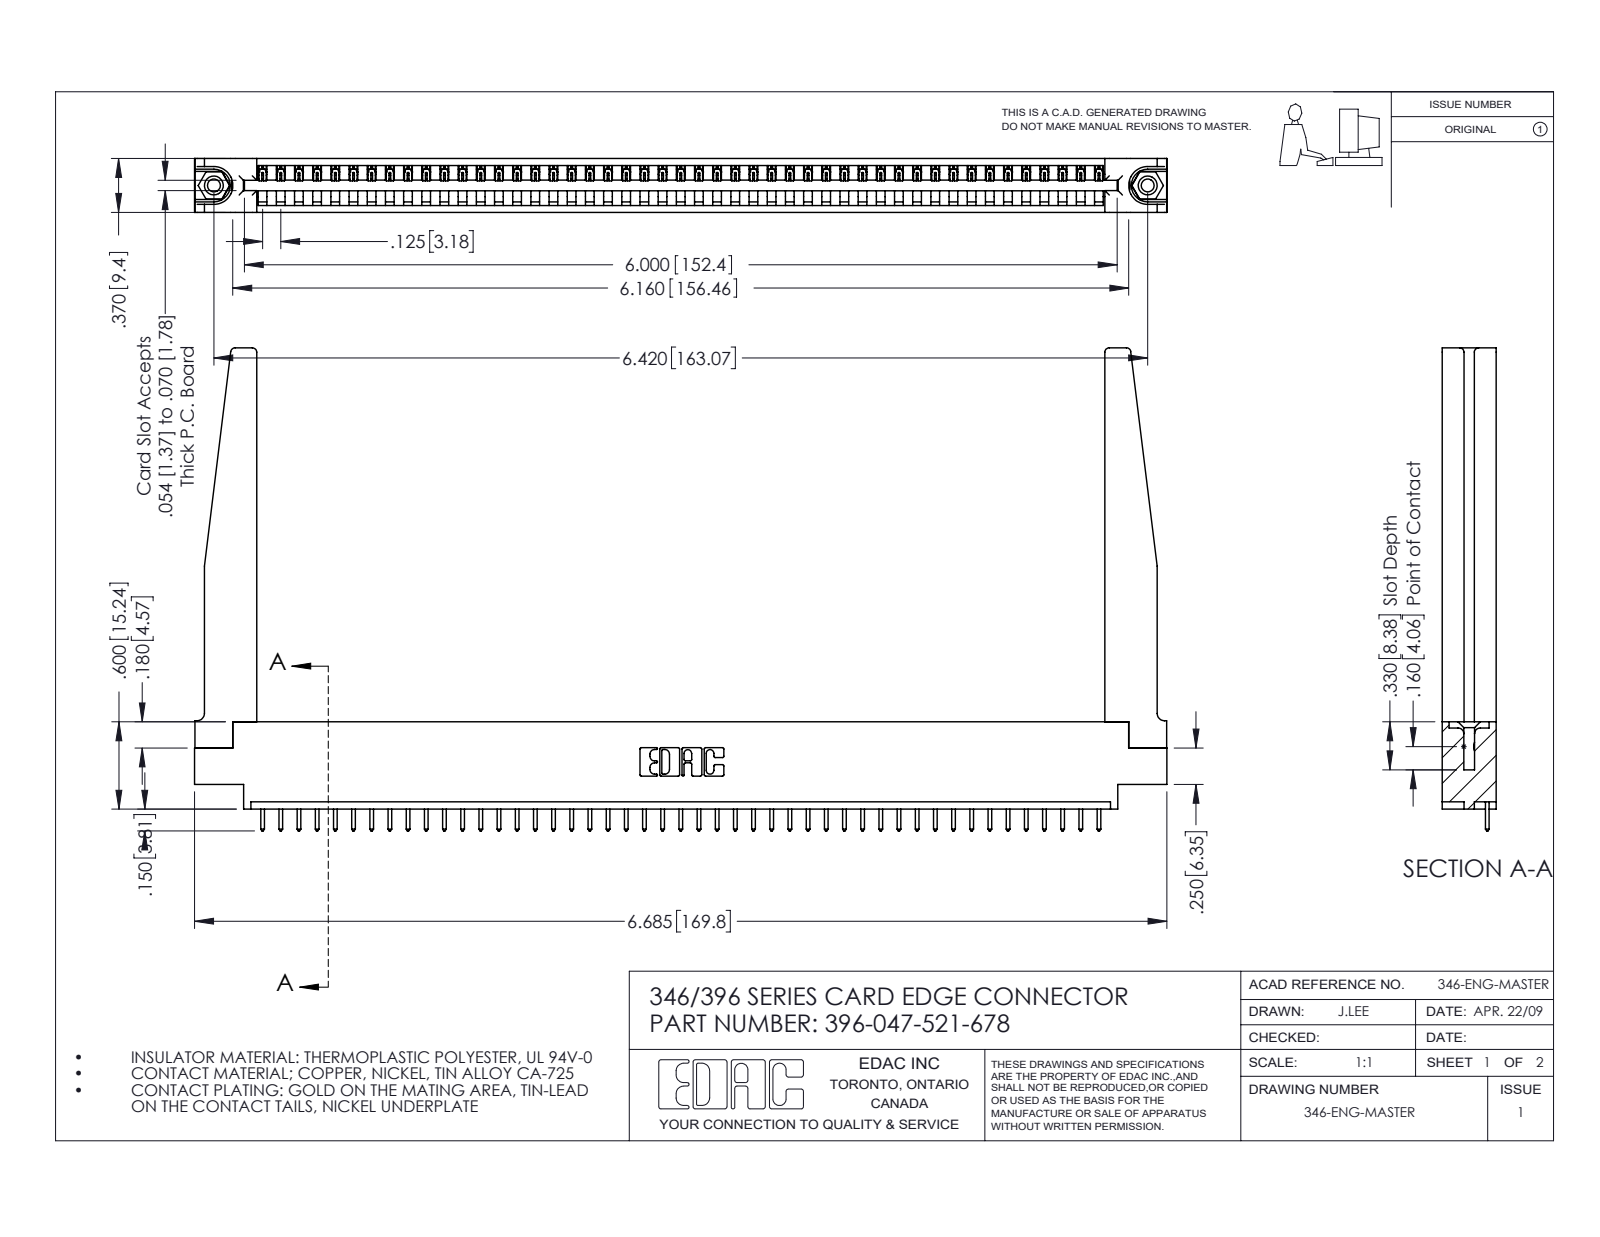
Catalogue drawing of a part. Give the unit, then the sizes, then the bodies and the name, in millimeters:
Units: millimetres
Overall size (bounding box): 169.8 × 84.3 × 9.4
Round holes (diameter × count): ⌀2.3 ×2, ⌀3.2 ×2, ⌀4 ×2, ⌀1.6 ×1
Round bosses / shafts (diameter × count): ⌀3.9 ×2
Partial cylindrical surfaces — rounded edges, fillets, slot ends (radius × count): R0.2 ×94, R0.3 ×94, R0.3 ×22, R0.8 ×8, R0.2 ×6, R0.8 ×6, R0.7 ×3, R0.8 ×2
Main face-to-face distances: 9.4, 1.2, 8.2, 1.8, 3.8, 3.8, 6.4, 7.6, 0.6, 5.6
Hole centre spacings: 6.2, 157.8, 163.1
Volume: 22 910 mm³ · Surface area: 26 220 mm²
Bodies: 52 solids, 3086 faces (2102 planar, 932 cylindrical, 52 other)
Part name (STEP PRODUCT): 345-250-001_345-250-001-102; 346 Part_0.170 Offset - 0.156 Dia-TH; 345-292-001_345-293-121; 346-220-078_345-220-078 (+1 more)
STEP written by: SolidWorks 2016 (CONFIG_CONTROL_DESIGN)
